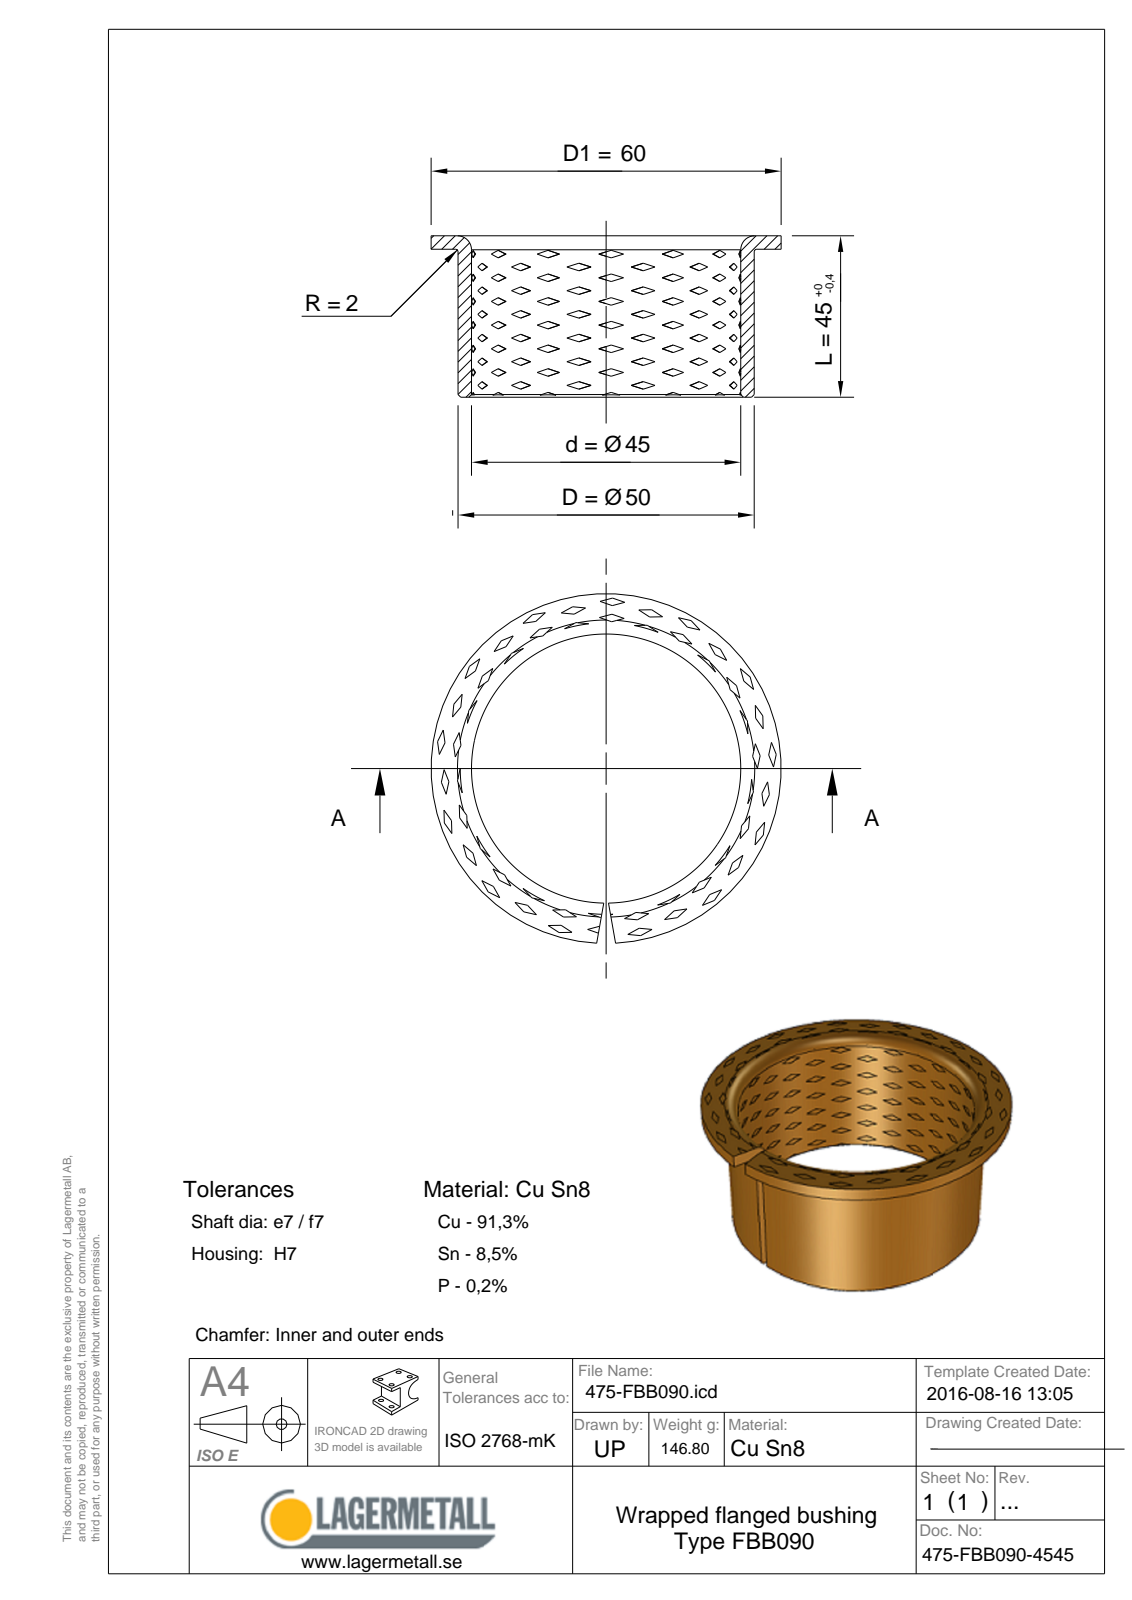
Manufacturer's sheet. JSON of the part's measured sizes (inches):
{"part_name": "475-FBB090-4545", "step_written_by": "Spatial InterOp 3D (CONFIG_CONTROL_DESIGN)", "units": "inches", "bodies": {"solids": 1, "faces": 12, "planar": 5, "cylindrical": 3, "other": 4}, "overall_size": [2.362, 2.36, 1.772], "volume_in3": 1.106, "surface_area_in2": 24.06, "round_holes": [[1.772, 1]], "round_bosses_or_shafts": [[2.362, 1], [1.969, 1]], "face_to_face_distances": [0.098, 1.673, 1.772]}
